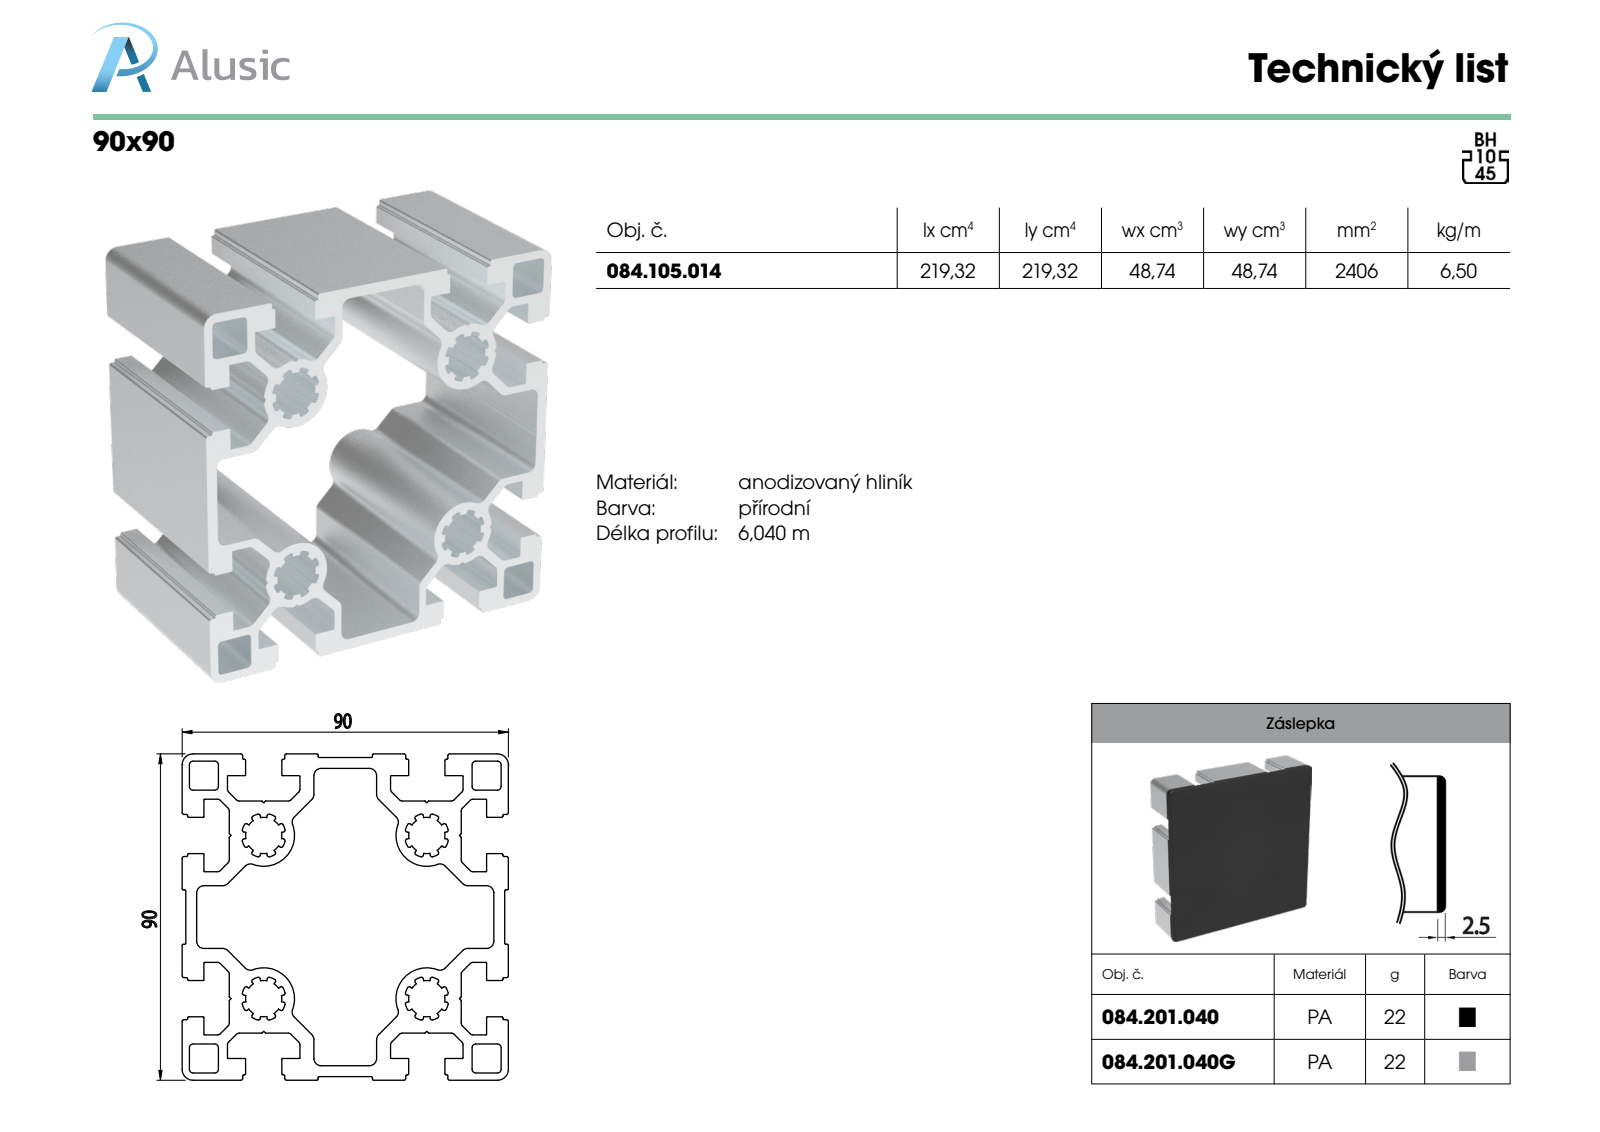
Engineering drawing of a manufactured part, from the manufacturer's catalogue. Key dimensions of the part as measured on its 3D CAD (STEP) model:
Part name (STEP PRODUCT): 084.105.014
STEP written by: SolidWorks 2018 (AUTOMOTIVE_DESIGN)
Units: millimetres
Bodies: 1 solid, 612 faces (258 planar, 354 cylindrical, 0 other)
Overall size (bounding box): 100 × 90 × 90
Volume: 240 596 mm³ · Surface area: 134 213 mm²
Partial cylindrical surfaces — rounded edges, fillets, slot ends (radius × count): R0.5 ×80, R0.3 ×48, R1 ×48, R0.2 ×32, R0.1 ×24, R2 ×24, R3 ×4, R5 ×4
Main face-to-face distances: 4, 2, 6, 84, 76, 1, 80, 9, 3, 13
